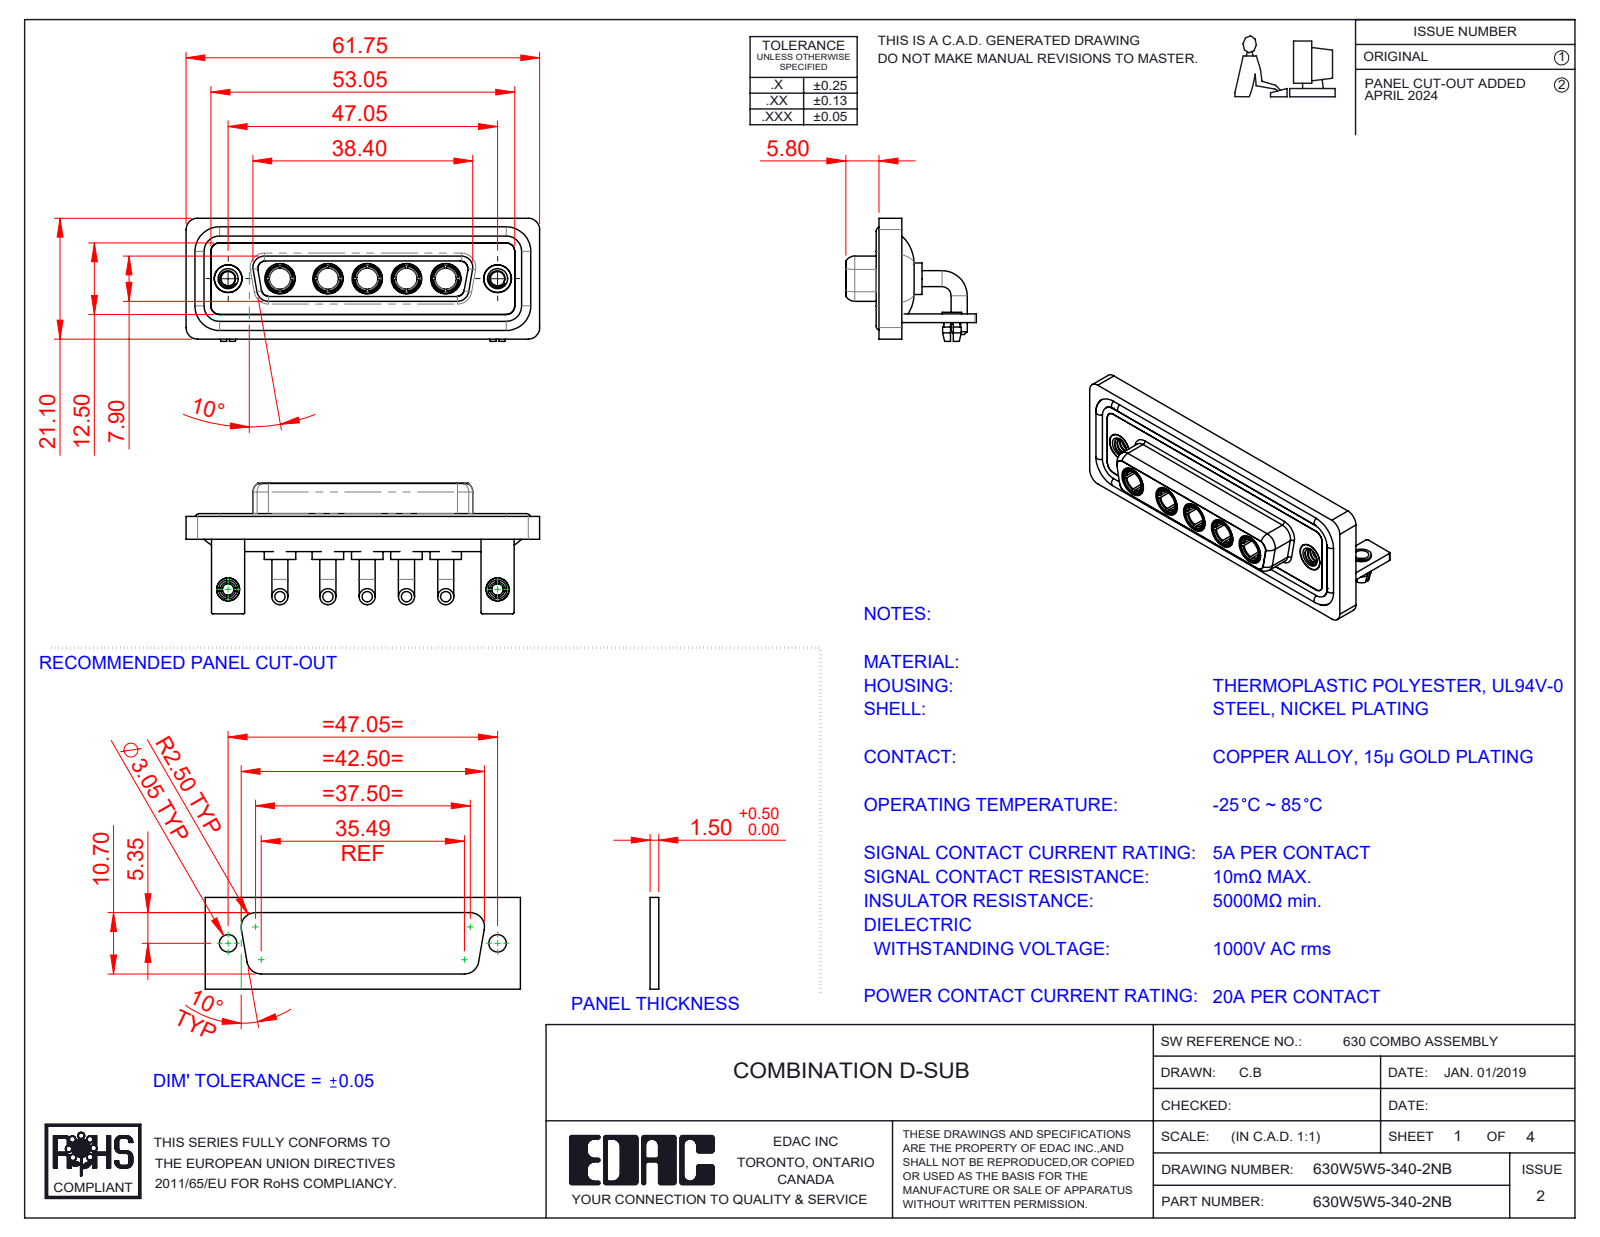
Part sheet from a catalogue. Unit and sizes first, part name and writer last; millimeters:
Units: millimetres
Overall size (bounding box): 61.75 × 22.8 × 21.5
Round holes (diameter × count): ⌀4.85 ×7, ⌀3.7 ×5, ⌀5.3 ×5, ⌀2.5 ×4, ⌀2 ×2, ⌀3.2 ×2, ⌀4 ×2, ⌀4.05 ×2, ⌀5 ×2
Round bosses / shafts (diameter × count): ⌀2.8 ×10, ⌀5.5 ×5, ⌀5.2 ×5, ⌀4.96 ×5, ⌀4.75 ×5, ⌀3.75 ×5, ⌀1.6 ×4, ⌀4.95 ×2
Partial cylindrical surfaces — rounded edges, fillets, slot ends (radius × count): R2 ×19, R1.5 ×18, R0.25 ×16, R1.35 ×8, R1.6 ×8, R0.5 ×5, R2.1 ×5, R0.6 ×4
Main face-to-face distances: 0.4, 1.8, 2.9, 1.5, 3.7, 4.1, 1.1, 1.4, 1.6, 2.5
Hole centre spacings: 6.86, 9.04, 38.01, 47.05, 6.87, 8.38, 13.72, 13.73
Volume: 8 830 mm³ · Surface area: 14 762 mm²
Bodies: 21 solids, 910 faces (318 planar, 367 cylindrical, 225 other)
Part name (STEP PRODUCT): 630Combo Threaded Rivet_A; 630W5W5-340-2NB; 630Combo Stabilizer Bracket_50 Contacts; Power Socket_20A RA (+5 more)
STEP written by: SolidWorks 2023 (CONFIG_CONTROL_DESIGN)
